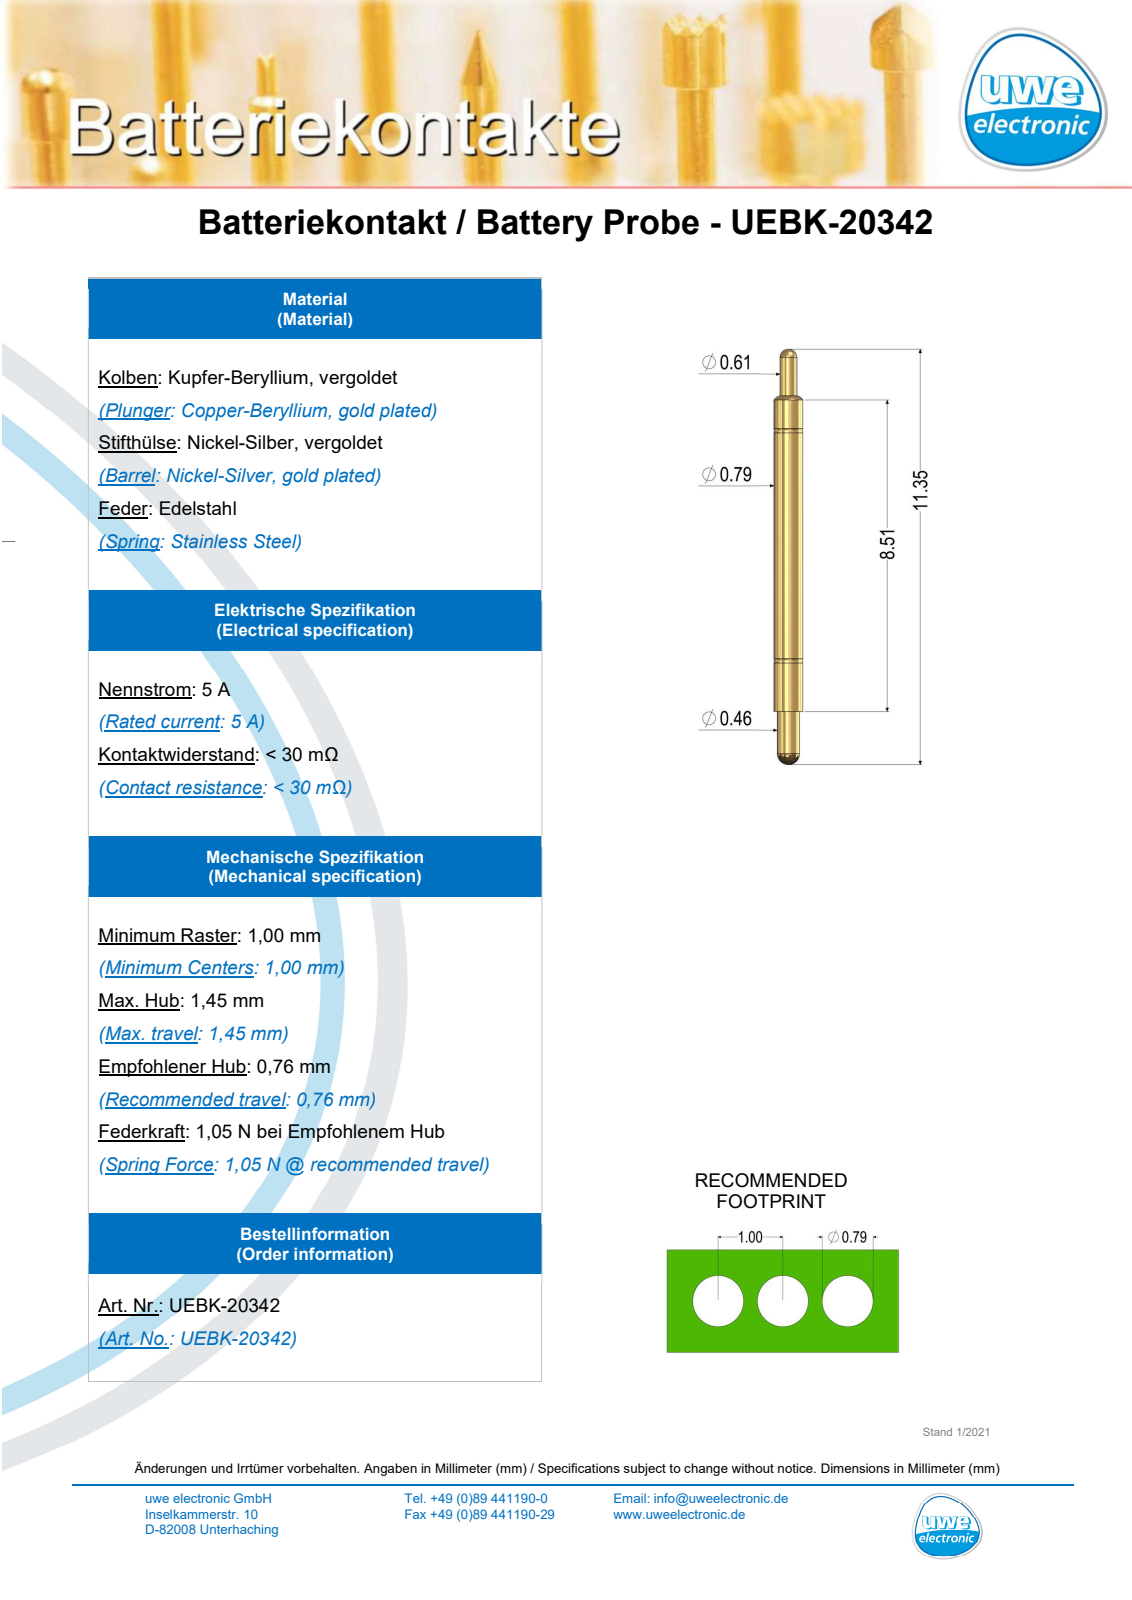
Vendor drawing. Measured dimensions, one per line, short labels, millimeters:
name: UEBK-20342_2017_09_05
written by: SolidWorks 2017 (AUTOMOTIVE_DESIGN)
unit: mm
bodies: 1 solid, 25 faces (1 planar, 10 cylindrical, 14 other)
size: 11.35 × 0.79 × 0.79
volume: 5 mm³; area: 26 mm²
bosses: 1× ⌀0.79, 1× ⌀0.61, 1× ⌀0.46
